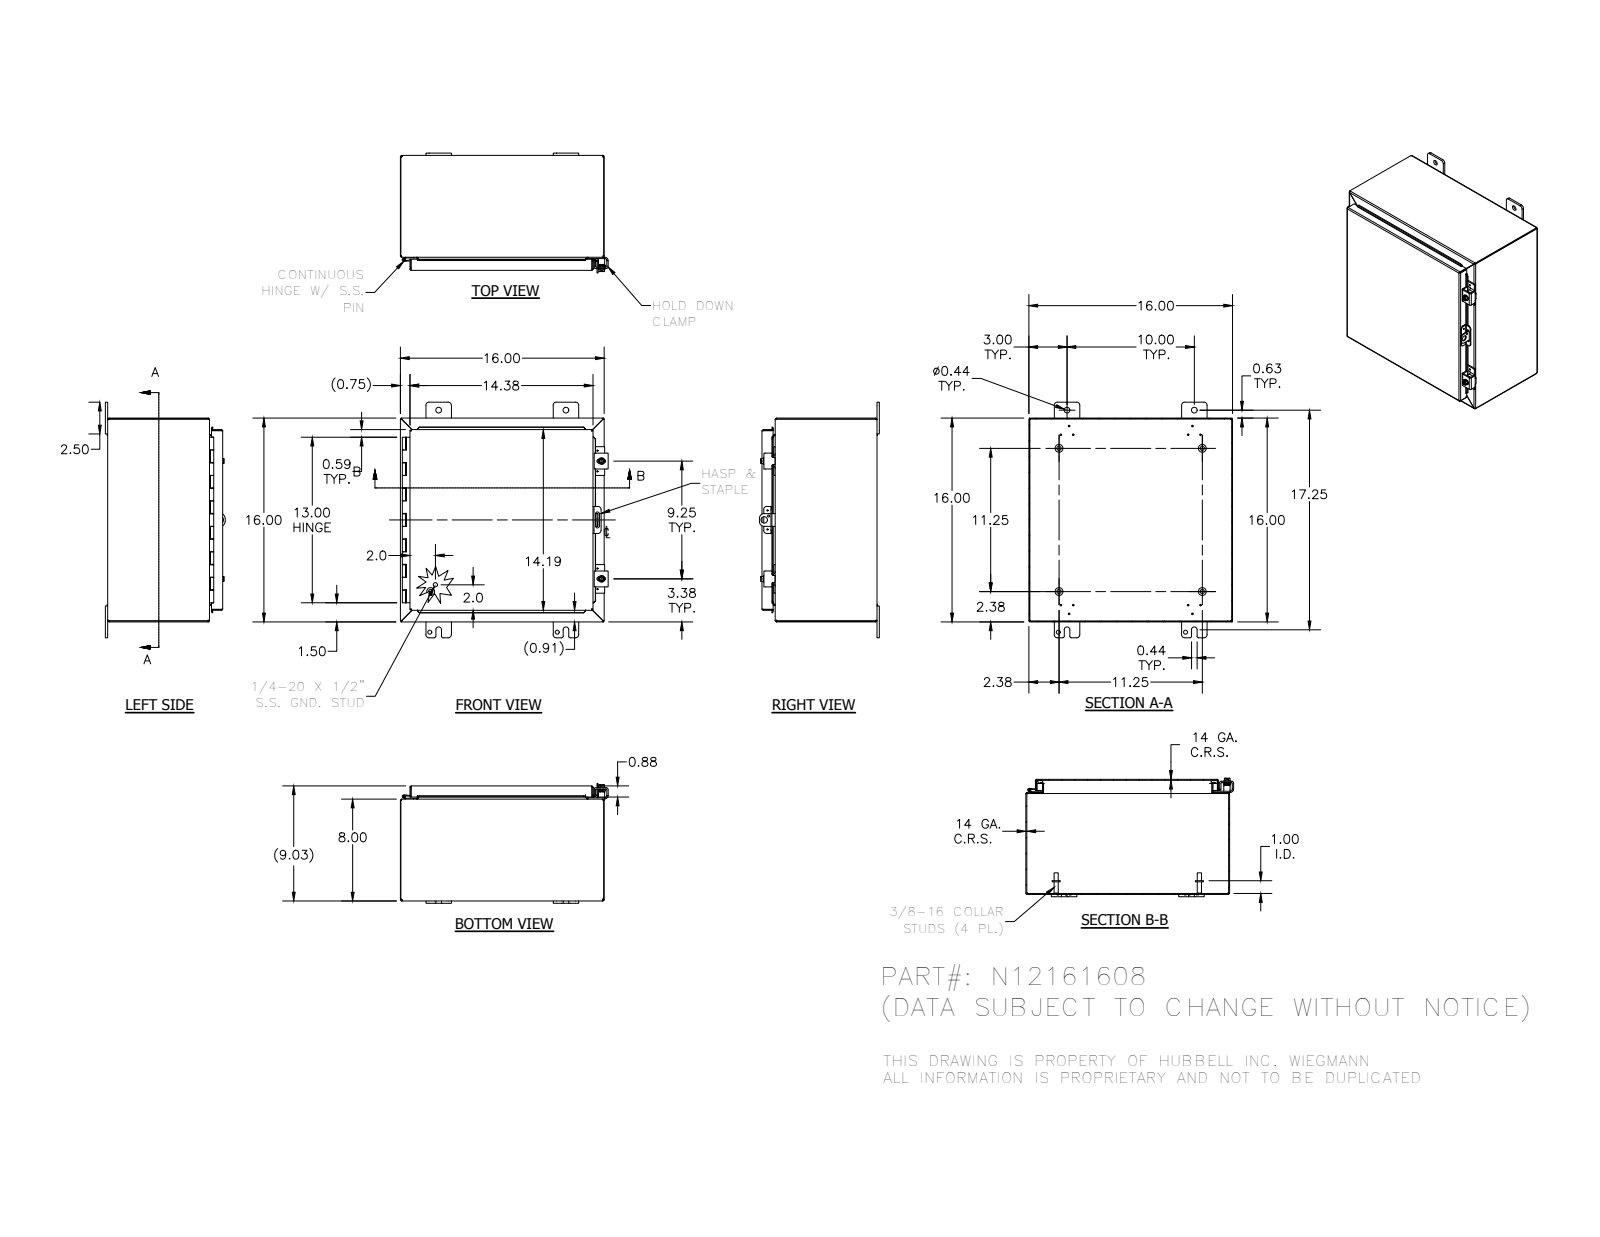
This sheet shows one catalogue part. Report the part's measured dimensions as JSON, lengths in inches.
{"part_name": "N12161608; 34840; 38420; N12161608BKP (+8 more)", "step_written_by": "Autodesk Inventor 2012 (AUTOMOTIVE_DESIGN)", "units": "inches", "bodies": {"solids": 27, "faces": 914, "planar": 489, "cylindrical": 308, "other": 117}, "overall_size": [18.5, 16.311, 9.41], "volume_in3": 97.28, "surface_area_in2": 2515, "round_holes": [[0.12, 12], [0.11, 7], [0.313, 4], [0.438, 4], [0.211, 2], [0.281, 2], [0.3, 2], [0.125, 1], [0.156, 1], [0.5, 1]], "round_bosses_or_shafts": [[0.625, 4], [0.33, 4], [0.25, 4], [0.52, 2], [0.5, 2], [0.35, 2], [0.115, 2], [0.337, 1]], "partial_cylinders_radius": [[0.03, 27], [0.063, 25], [0.125, 25], [0.25, 25], [0.031, 23], [0.105, 23], [0.07, 8], [0.1, 4]], "face_to_face_distances": [0.074, 15.926, 8.959, 16, 15.852, 8.885, 9.033, 7.926, 1.033, 8], "hole_center_spacings": [10, 0.759, 0.839, 0.94, 0.969, 1.593, 1.995, 9.382]}
